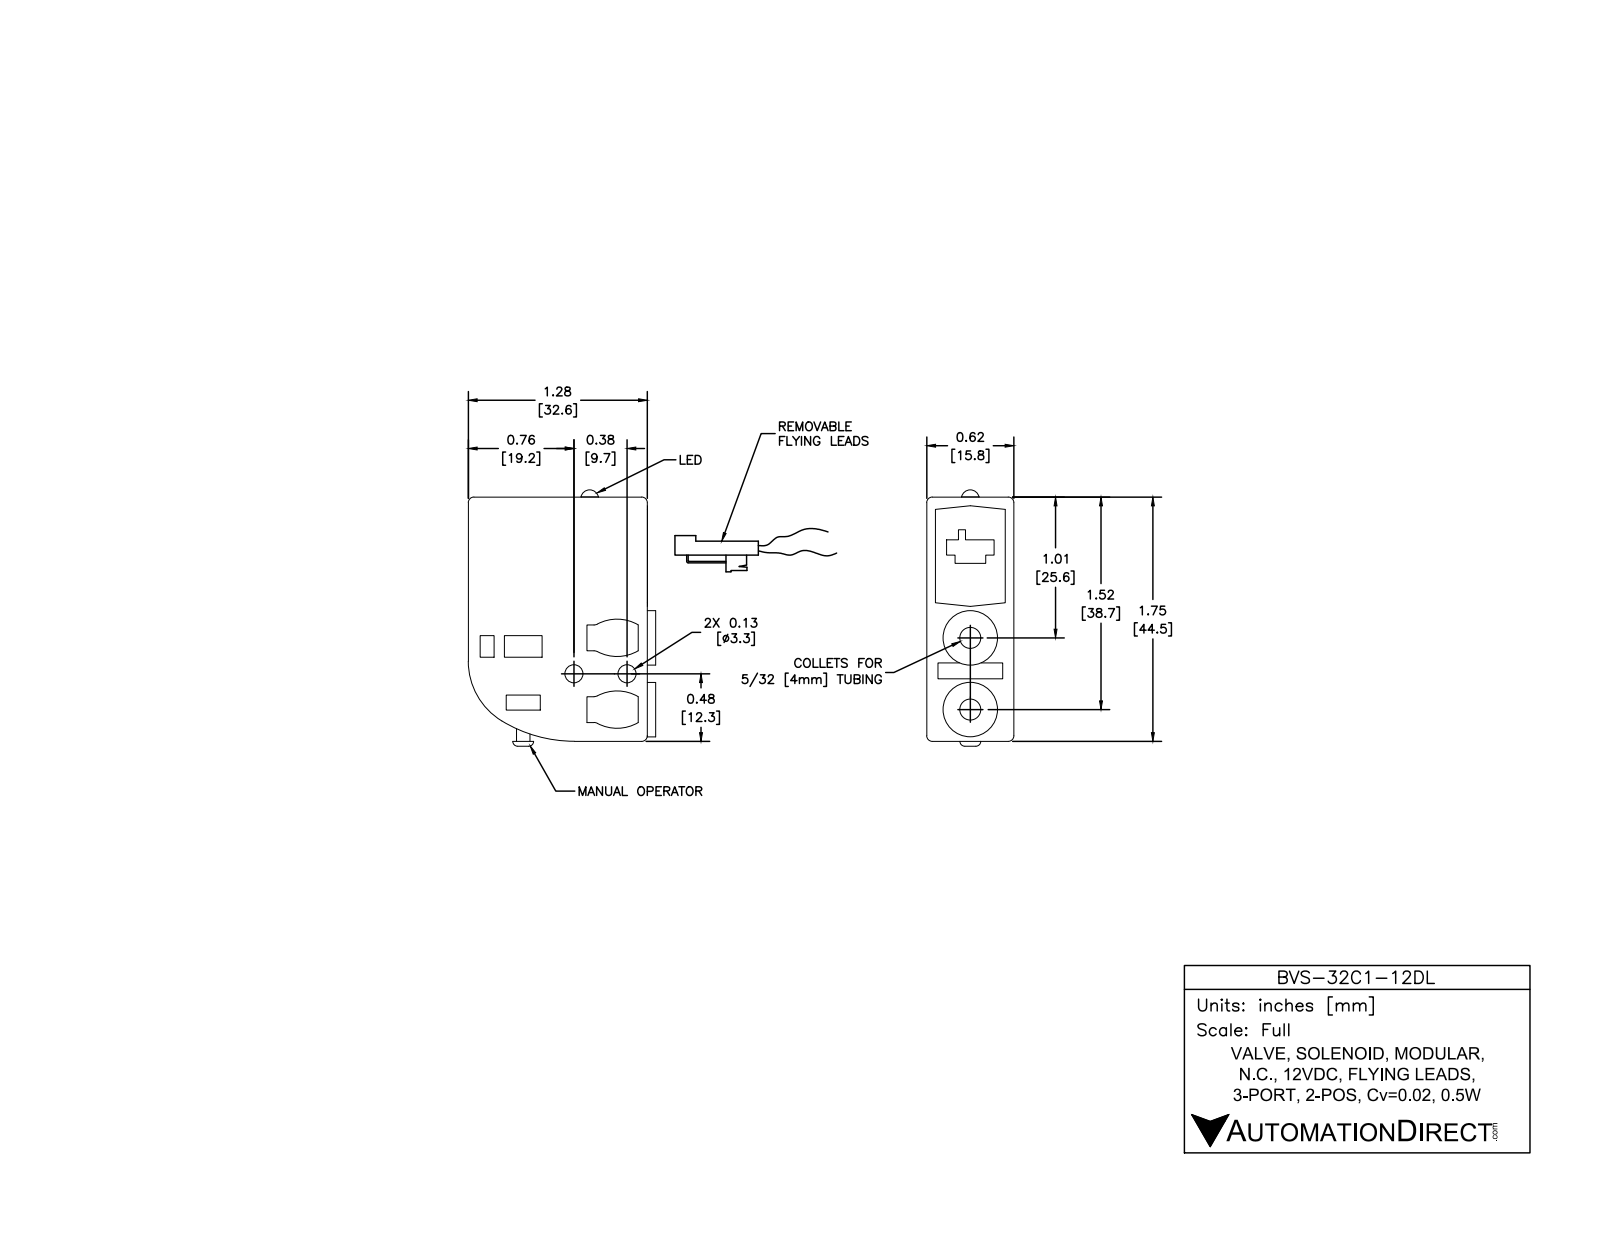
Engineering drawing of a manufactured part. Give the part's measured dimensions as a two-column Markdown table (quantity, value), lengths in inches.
| quantity | value |
| --- | --- |
| part name | BVS-32C1-12DL |
| STEP written by | SolidWorks 2016 (AUTOMOTIVE_DESIGN) |
| units | inches |
| bodies | 1 solid, 149 faces (83 planar, 54 cylindrical, 12 other) |
| overall size | 1.84 × 1.788 × 0.62 |
| volume | 1.259 in³ |
| surface area | 10.37 in² |
| round holes (diameter × count) | 0.13 × 2, 0.15 × 2, 0.25 × 2, 0.05 × 1 |
| round bosses / shafts (diameter × count) | 0.06 × 6, 0.39 × 2, 0.1 × 1 |
| partial cylindrical surfaces (radius × count) | 0.05 × 4, 0.3 × 4, 0.04 × 3, 0.5 × 1, 1 × 1 |
| main face-to-face distances | 0.62, 0.1, 1.29, 0.52, 1.291, 1.75, 1, 0.15, 0.06, 1.35 |
| hole center spacings | 0.06, 0.38, 0.45, 0.51 |
